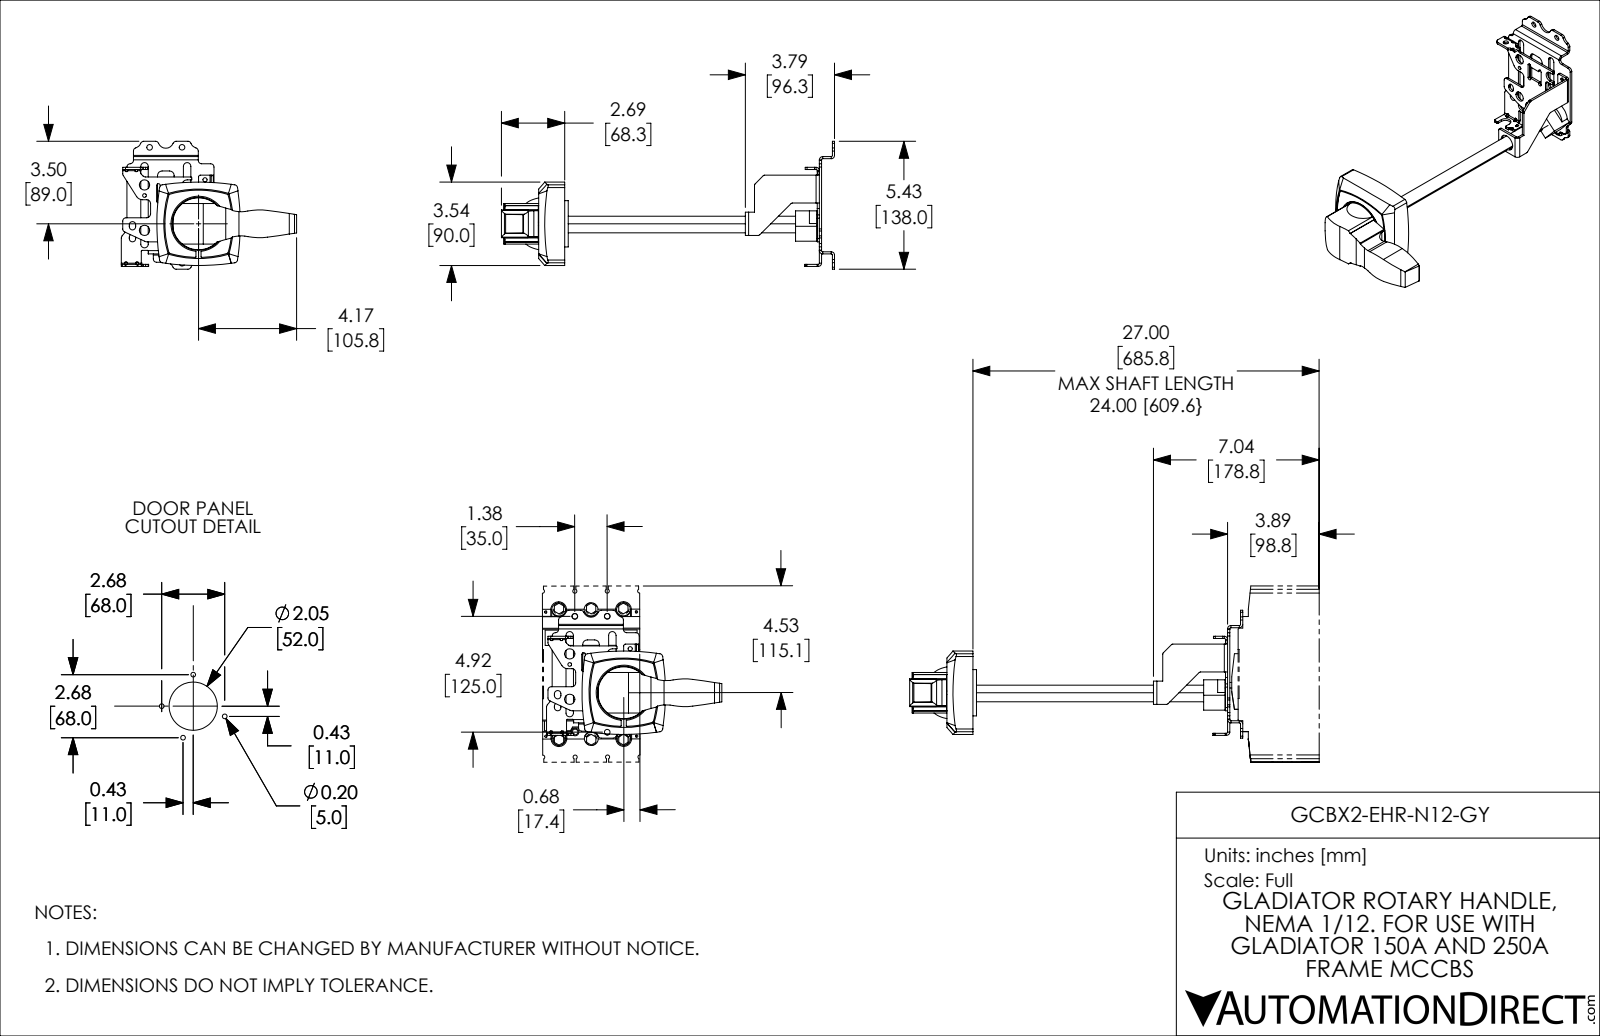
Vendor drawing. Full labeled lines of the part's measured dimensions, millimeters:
Part name (STEP PRODUCT): GCBX2-EHR-N12-GY
STEP written by: SolidWorks 2021 (CONFIG_CONTROL_DESIGN)
Units: millimetres
Bodies: 8 solids, 506 faces (241 planar, 106 cylindrical, 159 other)
Overall size (bounding box): 359.56 × 189.14 × 138
Volume: 428 243 mm³ · Surface area: 107 172 mm²
Round holes (diameter × count): ⌀5 ×4, ⌀6 ×3, ⌀50 ×1, ⌀57 ×1
Round bosses / shafts (diameter × count): ⌀59.5 ×1, ⌀50 ×1, ⌀11 ×1
Partial cylindrical surfaces — rounded edges, fillets, slot ends (radius × count): R0.5 ×12, R1.27 ×8, R3.57 ×8, R3 ×4, R3.5 ×4, R113.75 ×4, R257.5 ×4, R262 ×4
Main face-to-face distances: 2.3, 12.7, 278.88, 276.58, 4.6, 274.28, 16.3, 14, 301.78, 299.48
Hole centre spacings: 34, 35.74, 68.88, 10.93, 35, 41.05, 45.51, 46.12
